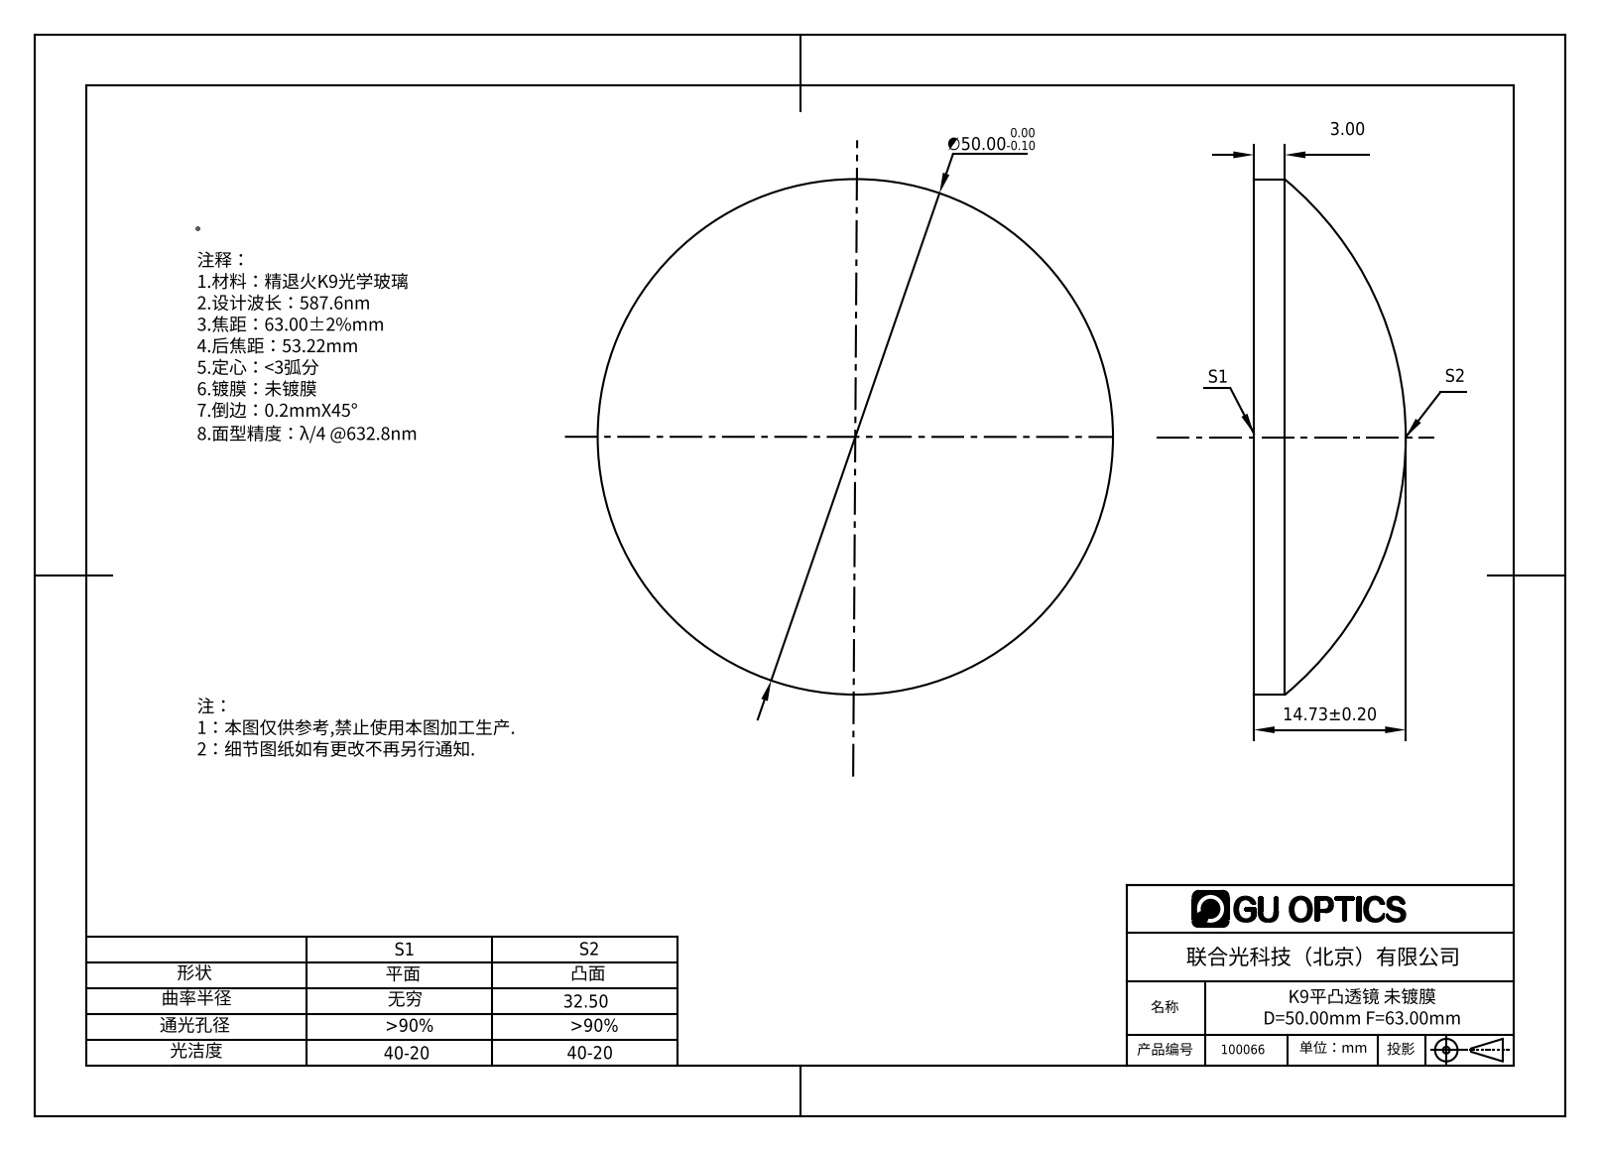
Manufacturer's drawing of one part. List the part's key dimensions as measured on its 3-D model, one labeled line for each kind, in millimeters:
Part name (STEP PRODUCT): 100066
STEP written by: SolidWorks 2016 (AUTOMOTIVE_DESIGN)
Units: millimetres
Bodies: 1 solid, 5 faces (1 planar, 2 cylindrical, 2 other)
Overall size (bounding box): 50 × 50 × 14.73
Volume: 18 251 mm³ · Surface area: 4 830 mm²
Round bosses / shafts (diameter × count): ⌀50 ×1
